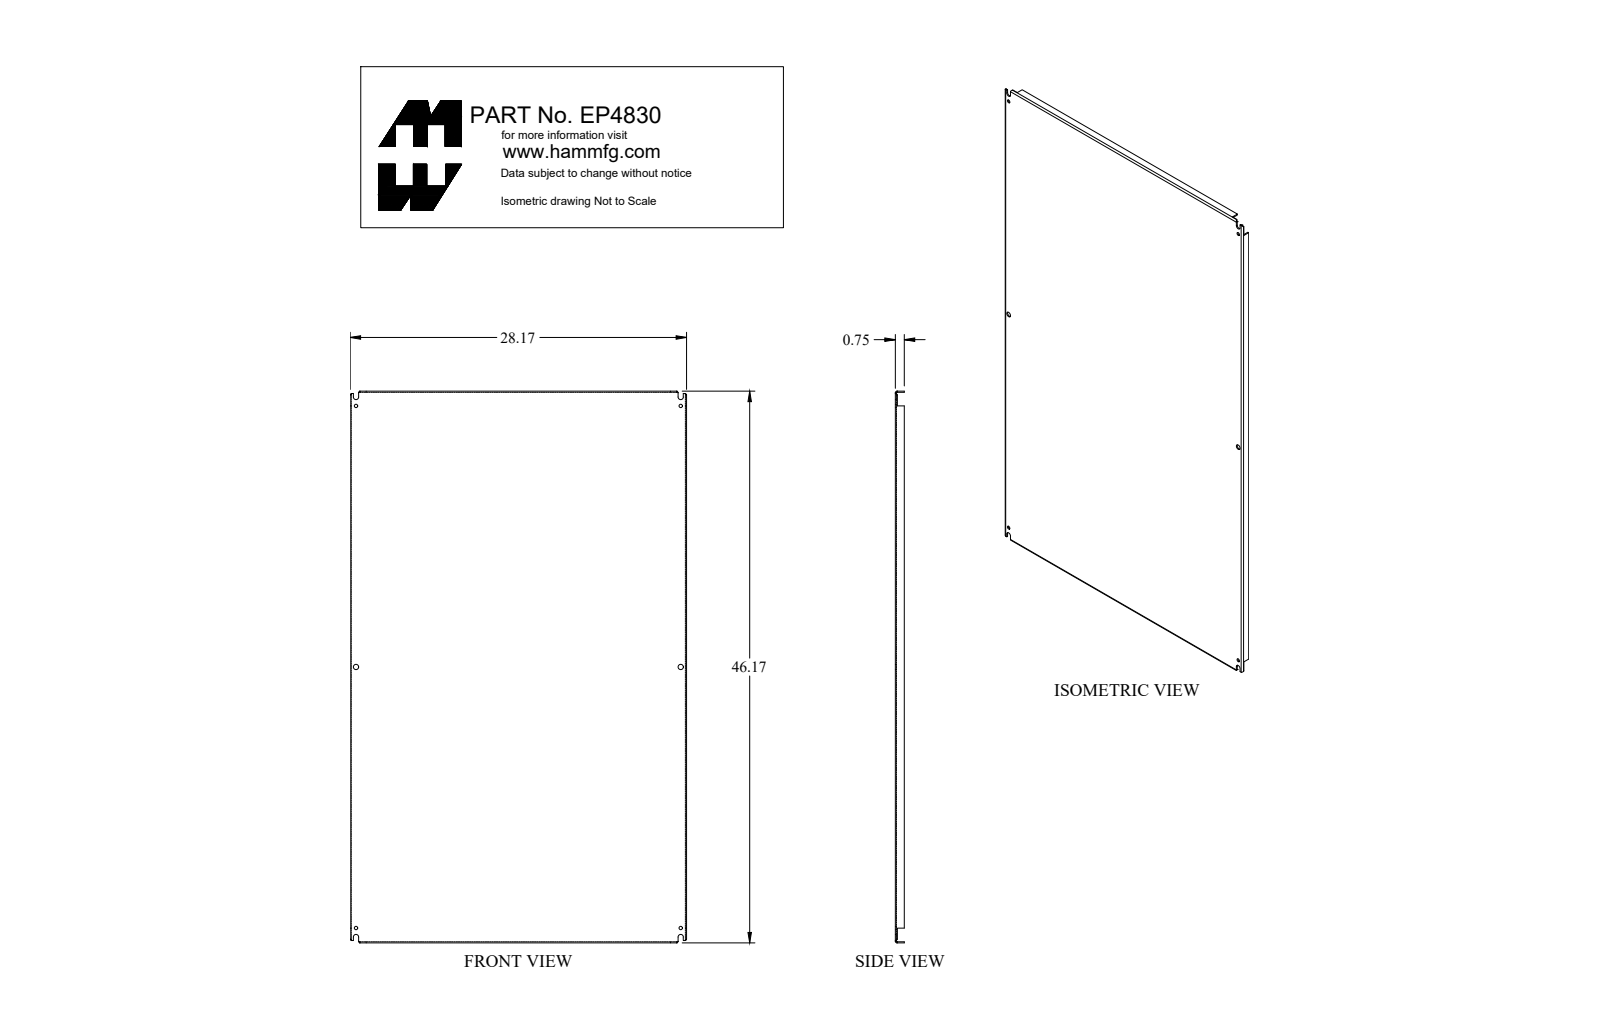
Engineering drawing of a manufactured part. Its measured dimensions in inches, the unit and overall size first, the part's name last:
Units: inches
Overall size (bounding box): 46.17 × 28.17 × 0.75
Round holes (diameter × count): ⌀0.281 ×4, ⌀0.437 ×2
Partial cylindrical surfaces — rounded edges, fillets, slot ends (radius × count): R0.048 ×4, R0.063 ×4, R0.143 ×4, R0.219 ×4
Main face-to-face distances: 0.095, 28.075, 46.075, 27.98, 28.17, 45.98, 46.17, 0.75, 0.655, 0.171
Hole centre spacings: 21.844, 34.876, 27.188, 43.688, 51.457
Volume: 131.4 in³ · Surface area: 2 783 in²
Bodies: 1 solid, 132 faces (74 planar, 42 cylindrical, 16 other)
Part name (STEP PRODUCT): EP4830
STEP written by: SolidWorks 2018 (AUTOMOTIVE_DESIGN)
